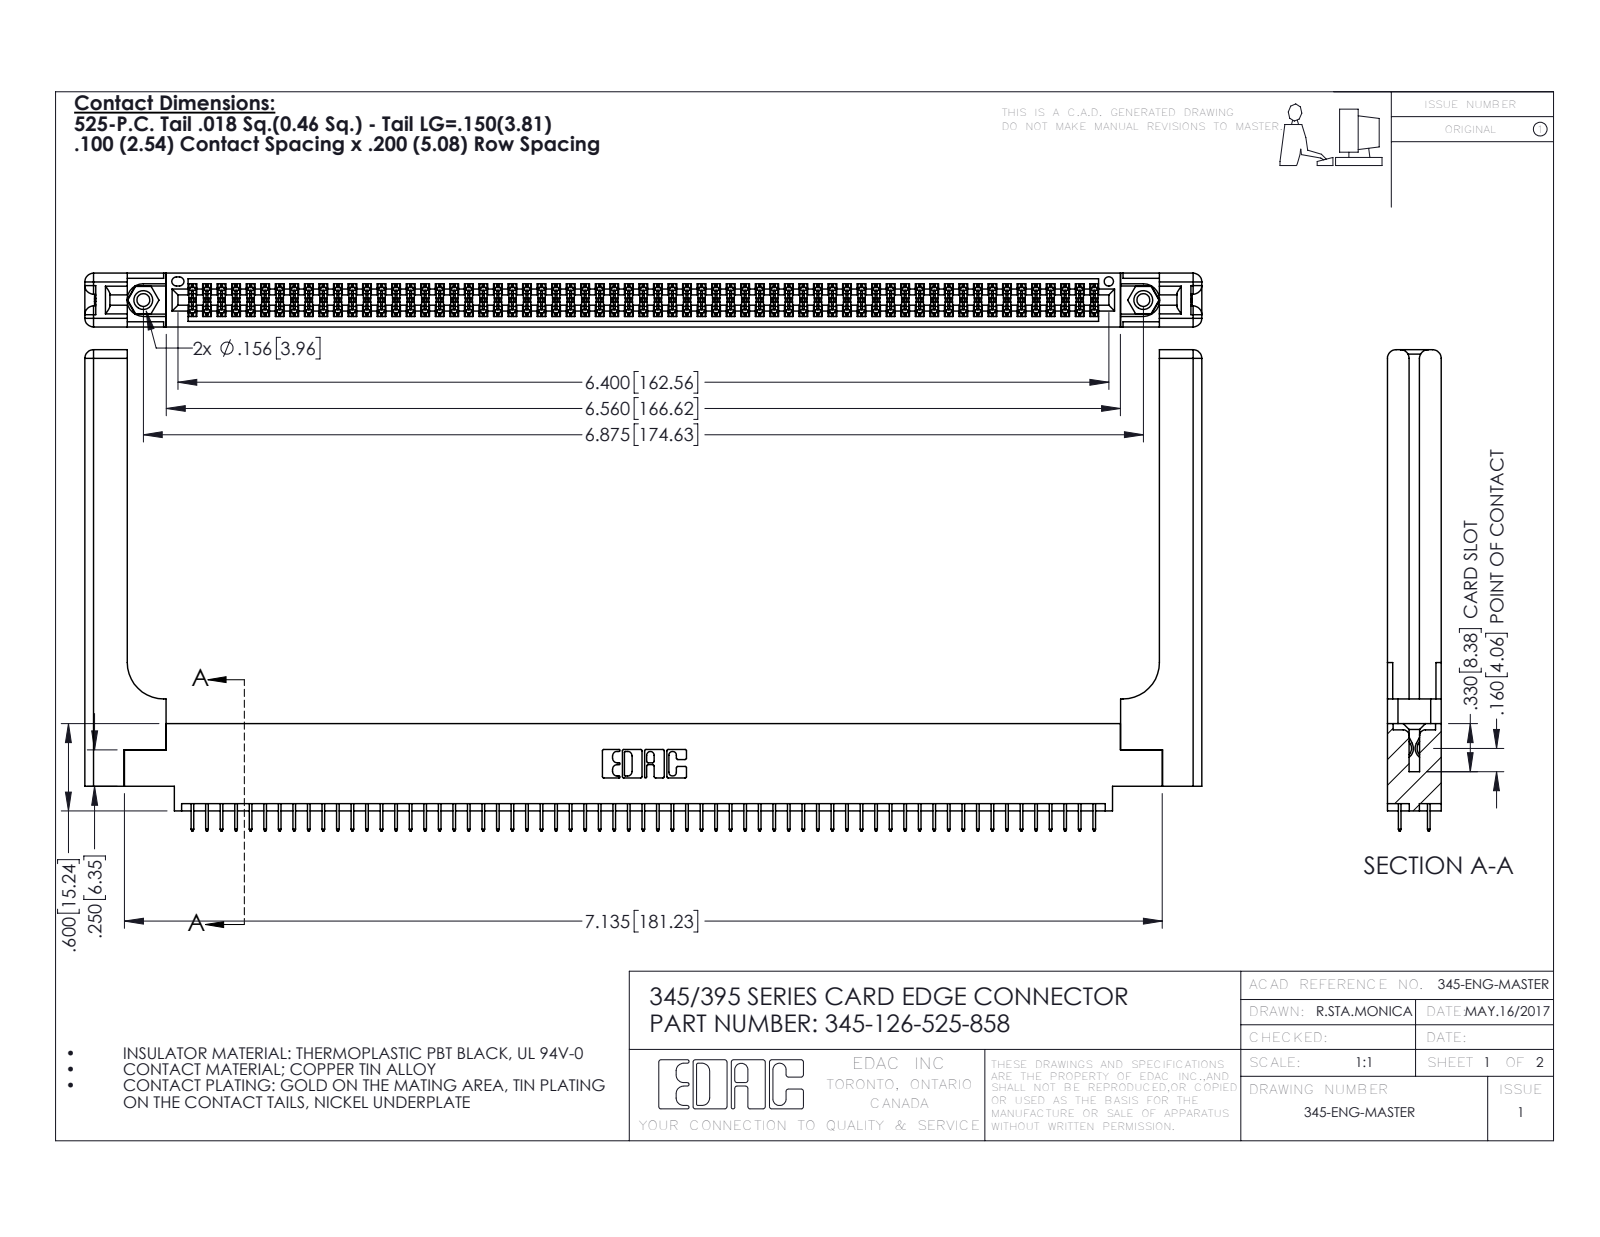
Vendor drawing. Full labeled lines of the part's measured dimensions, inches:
Part name (STEP PRODUCT): 345-292-001_345-293-125; 345-250-001_345-250-001-102; 345-126-525-858; 345-220-058_345-220-058 (+1 more)
STEP written by: SolidWorks 2020 (CONFIG_CONTROL_DESIGN)
Units: inches
Bodies: 131 solids, 7190 faces (5146 planar, 1984 cylindrical, 60 other)
Overall size (bounding box): 7.679 × 3.307 × 0.37
Volume: 1.666 in³ · Surface area: 50.85 in²
Round holes (diameter × count): ⌀0.089 ×2, ⌀0.125 ×2, ⌀0.156 ×2, ⌀0.064 ×1
Round bosses / shafts (diameter × count): ⌀0.155 ×2
Partial cylindrical surfaces — rounded edges, fillets, slot ends (radius × count): R0.006 ×189, R0.01 ×22, R0.06 ×16, R0.007 ×6, R0.031 ×6, R0.026 ×3, R0.014 ×2, R0.019 ×2
Main face-to-face distances: 0.072, 0.37, 0.298, 0.098, 0.272, 0.025, 0.2, 0.225, 0.175, 0.15
Hole centre spacings: 0.27, 6.639, 6.875
